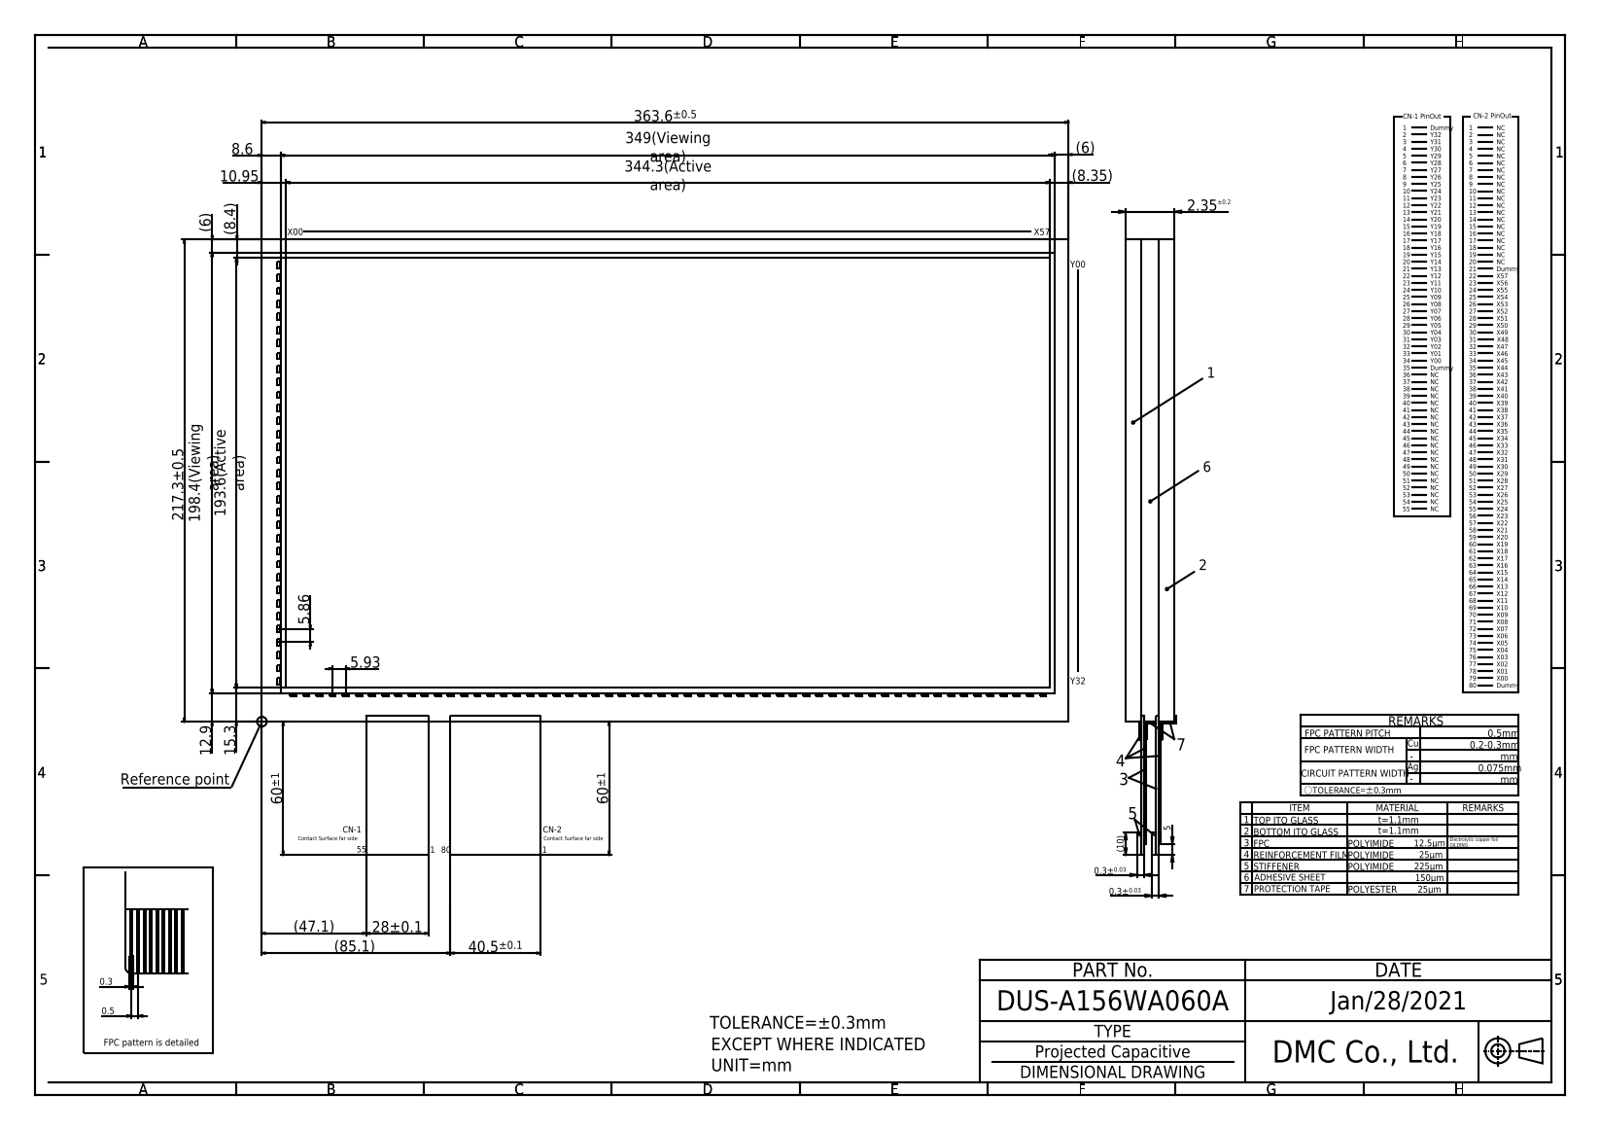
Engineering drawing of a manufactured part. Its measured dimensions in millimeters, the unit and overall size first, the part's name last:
Units: millimetres
Overall size (bounding box): 509.04 × 320.76 × 2.35
Partial cylindrical surfaces — rounded edges, fillets, slot ends (radius × count): R0.2 ×4
Main face-to-face distances: 2.35, 1.1, 1.2, 1.15, 1.25, 1, 2.25, 217.3, 0.8, 0.7
Volume: 185 996 mm³ · Surface area: 169 276 mm²
Bodies: 1 solid, 578 faces (574 planar, 4 cylindrical, 0 other)
Part name (STEP PRODUCT): DUS-A156WA060A
STEP written by: Autodesk Inventor 2020 (CONFIG_CONTROL_DESIGN)
